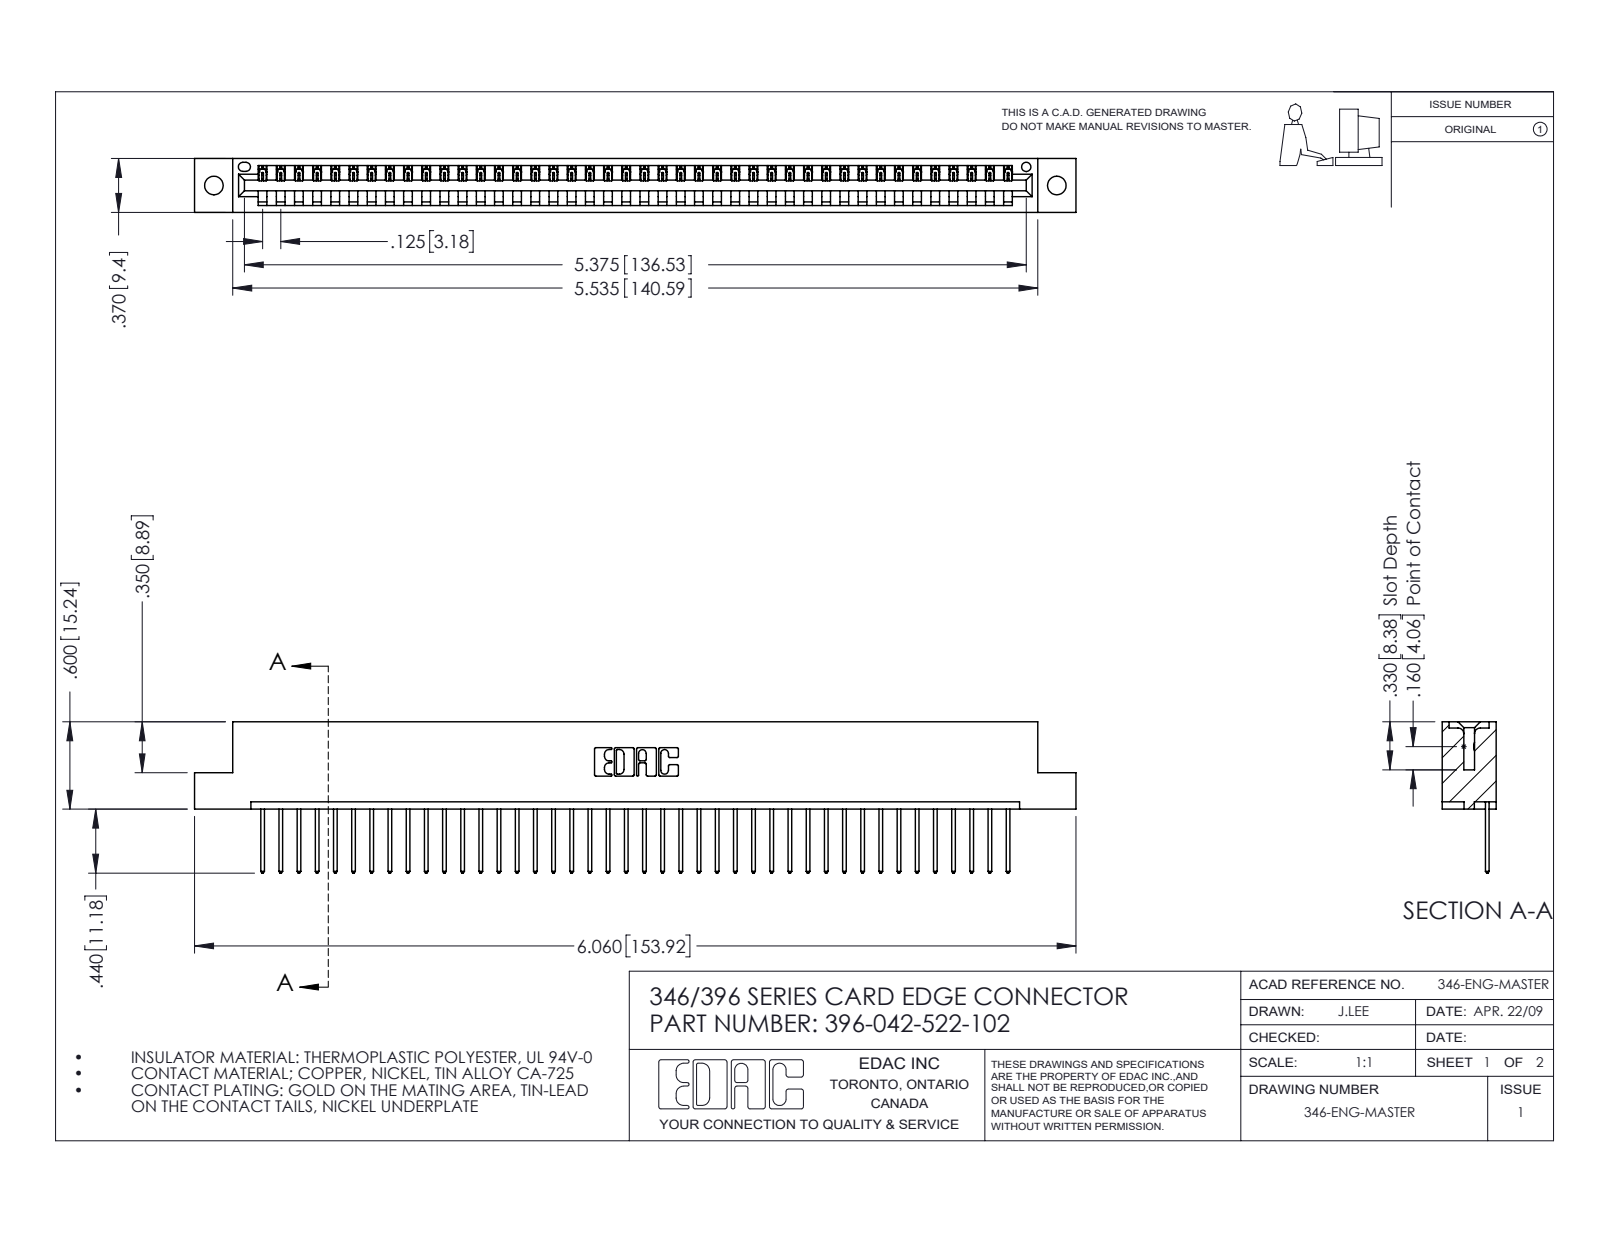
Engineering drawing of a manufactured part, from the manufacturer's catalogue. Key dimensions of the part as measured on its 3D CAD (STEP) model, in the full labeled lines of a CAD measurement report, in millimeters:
Part name (STEP PRODUCT): 396-042-522-102; 346 Part_Flush Mounting Lugs - 0.128 Dia; 345-292-001_345-293-122
STEP written by: SolidWorks 2016 (CONFIG_CONTROL_DESIGN)
Units: millimetres
Bodies: 43 solids, 2558 faces (1756 planar, 802 cylindrical, 0 other)
Overall size (bounding box): 153.9 × 26.4 × 9.4
Volume: 14 700 mm³ · Surface area: 18 260 mm²
Round holes (diameter × count): ⌀3.3 ×2, ⌀1.6 ×1
Partial cylindrical surfaces — rounded edges, fillets, slot ends (radius × count): R0.2 ×84, R0.3 ×84, R0.3 ×22, R0.2 ×6, R0.8 ×6, R0.7 ×3, R0.8 ×2, R1 ×2
Main face-to-face distances: 1.2, 8.2, 9.4, 6.4, 1.8, 7.6, 0.6, 3.8, 5.6, 2.5
Hole centre spacings: 6.2, 141.9, 147.2
